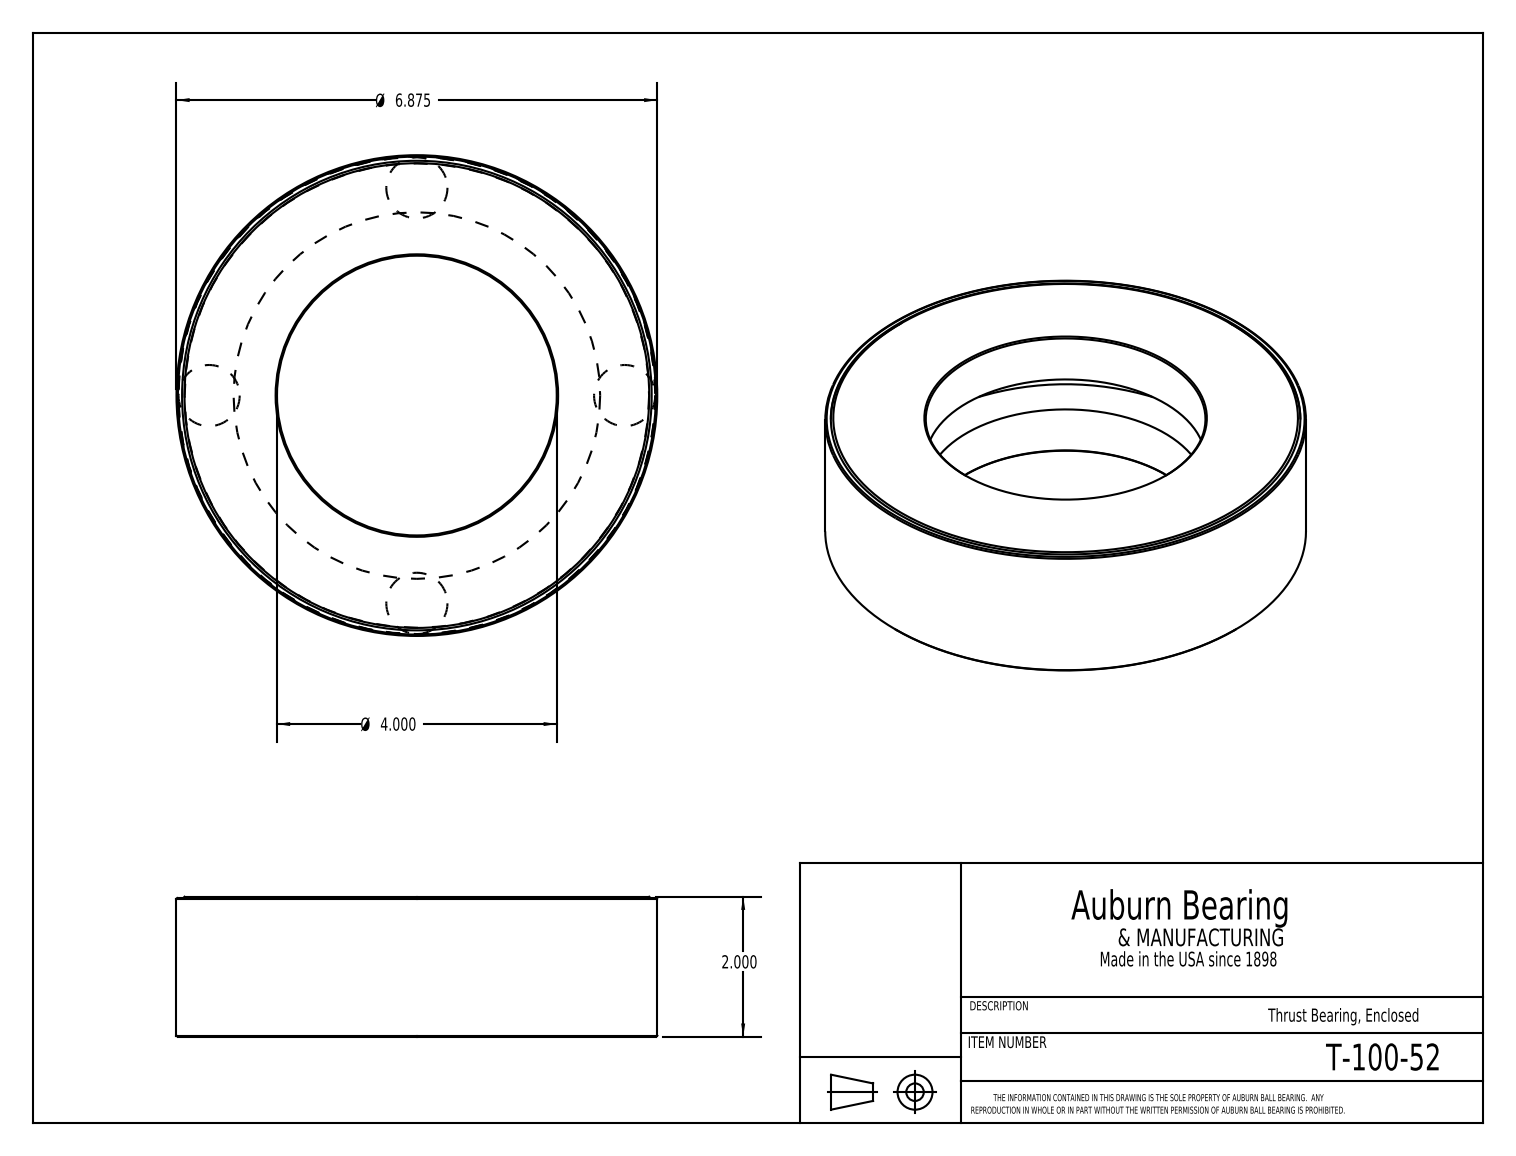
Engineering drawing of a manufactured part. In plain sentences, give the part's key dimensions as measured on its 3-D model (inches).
The part is named "T-100-52". Its 3-D file was written by "SolidWorks 2016 (CONFIG_CONTROL_DESIGN)". It is 6 solids with 28 faces: 9 planar, 7 cylindrical and 12 other. Overall it measures 6.875 by 6.875 by 2 inches. Its volume is 34.47 cubic inches and its surface area 215.8 square inches. Round holes: 1 of diameter 4, 1 of diameter 6.715, 1 of diameter 6.835. Round bosses or shafts: 1 of diameter 6.875, 1 of diameter 6.821. The main face-to-face distances are 0.737, 1.263, 2, 0.525, 1.965, 1.985, 1.228, 1.248, 0.702, 0.722.
